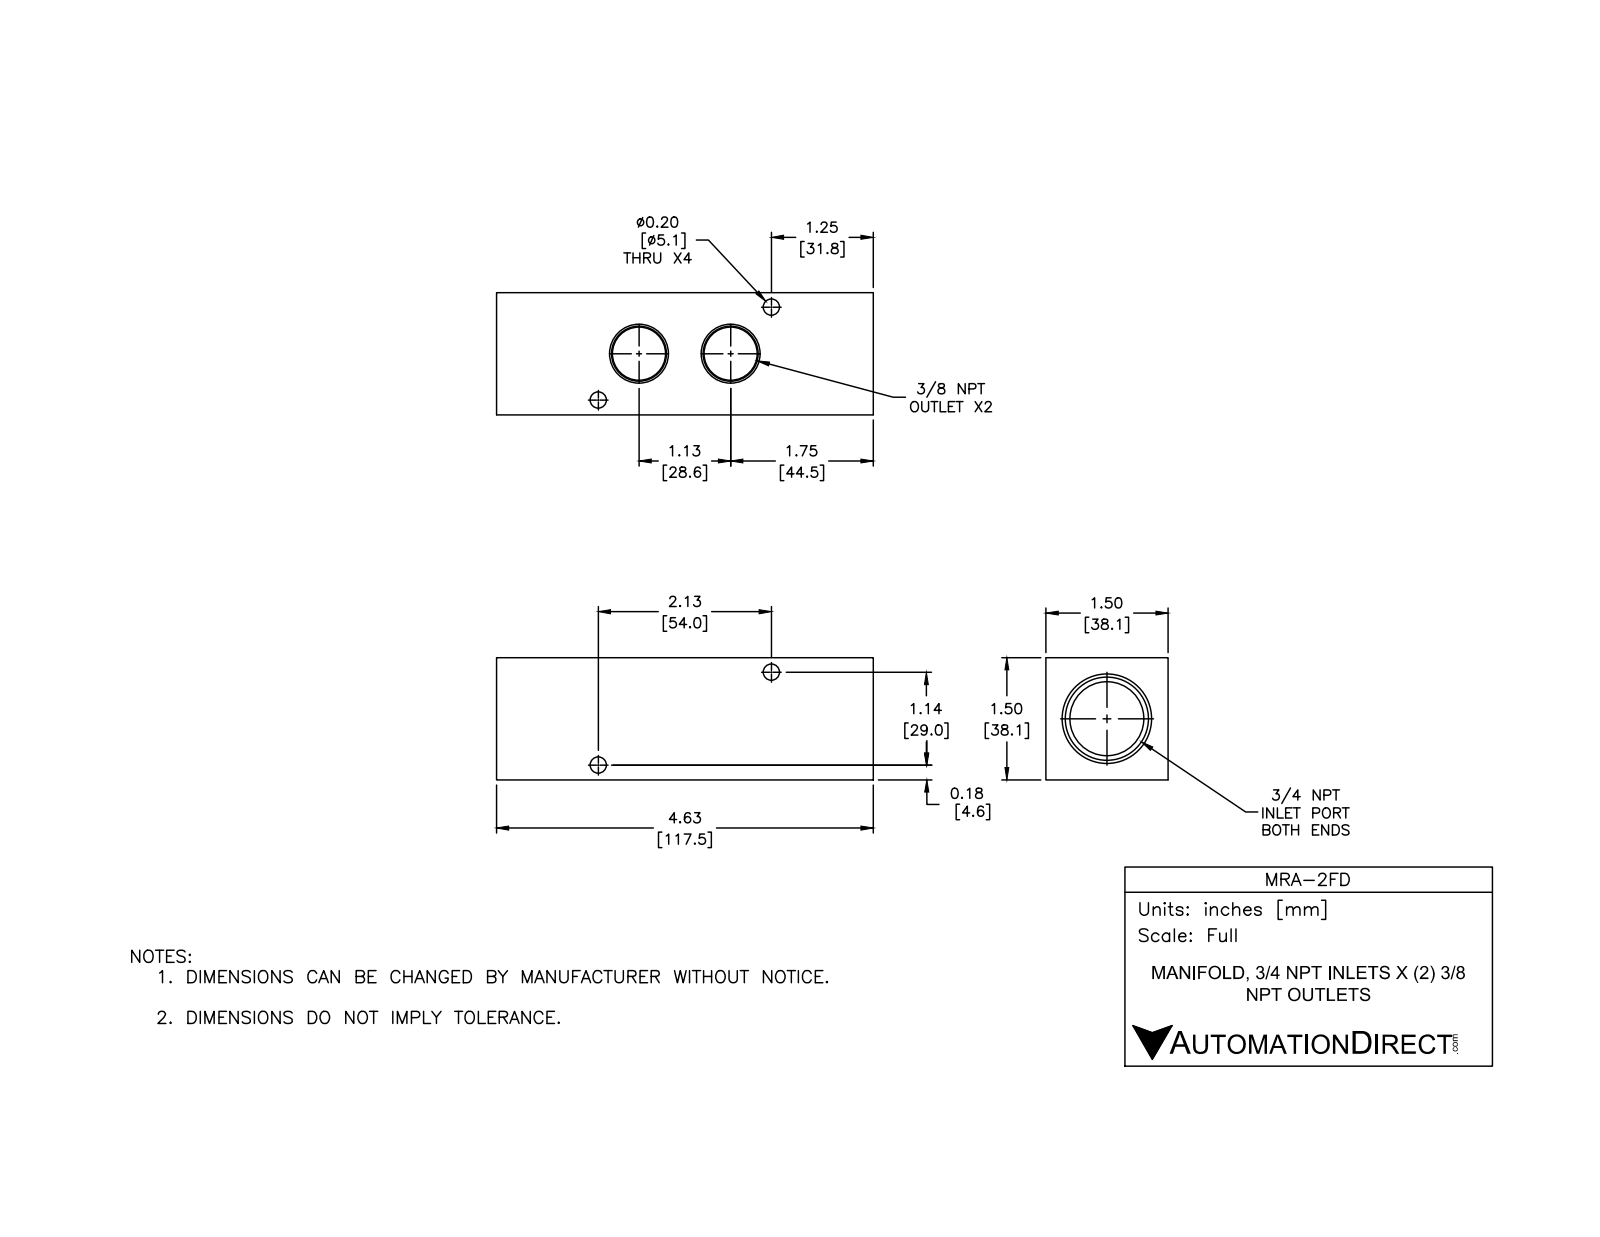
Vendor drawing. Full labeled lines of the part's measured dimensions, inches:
Part name (STEP PRODUCT): MRA-2FD
STEP written by: SolidWorks 2015 (CONFIG_CONTROL_DESIGN)
Units: inches
Bodies: 1 solid, 46 faces (12 planar, 18 cylindrical, 16 other)
Overall size (bounding box): 4.625 × 1.5 × 1.5
Volume: 6.798 in³ · Surface area: 47.61 in²
Round holes (diameter × count): ⌀0.2 ×4, ⌀0.906 ×1
Main face-to-face distances: 1.5, 4.625, 0.55, 4.075, 3.525, 1.09, 0.41
Hole centre spacings: 2.412
